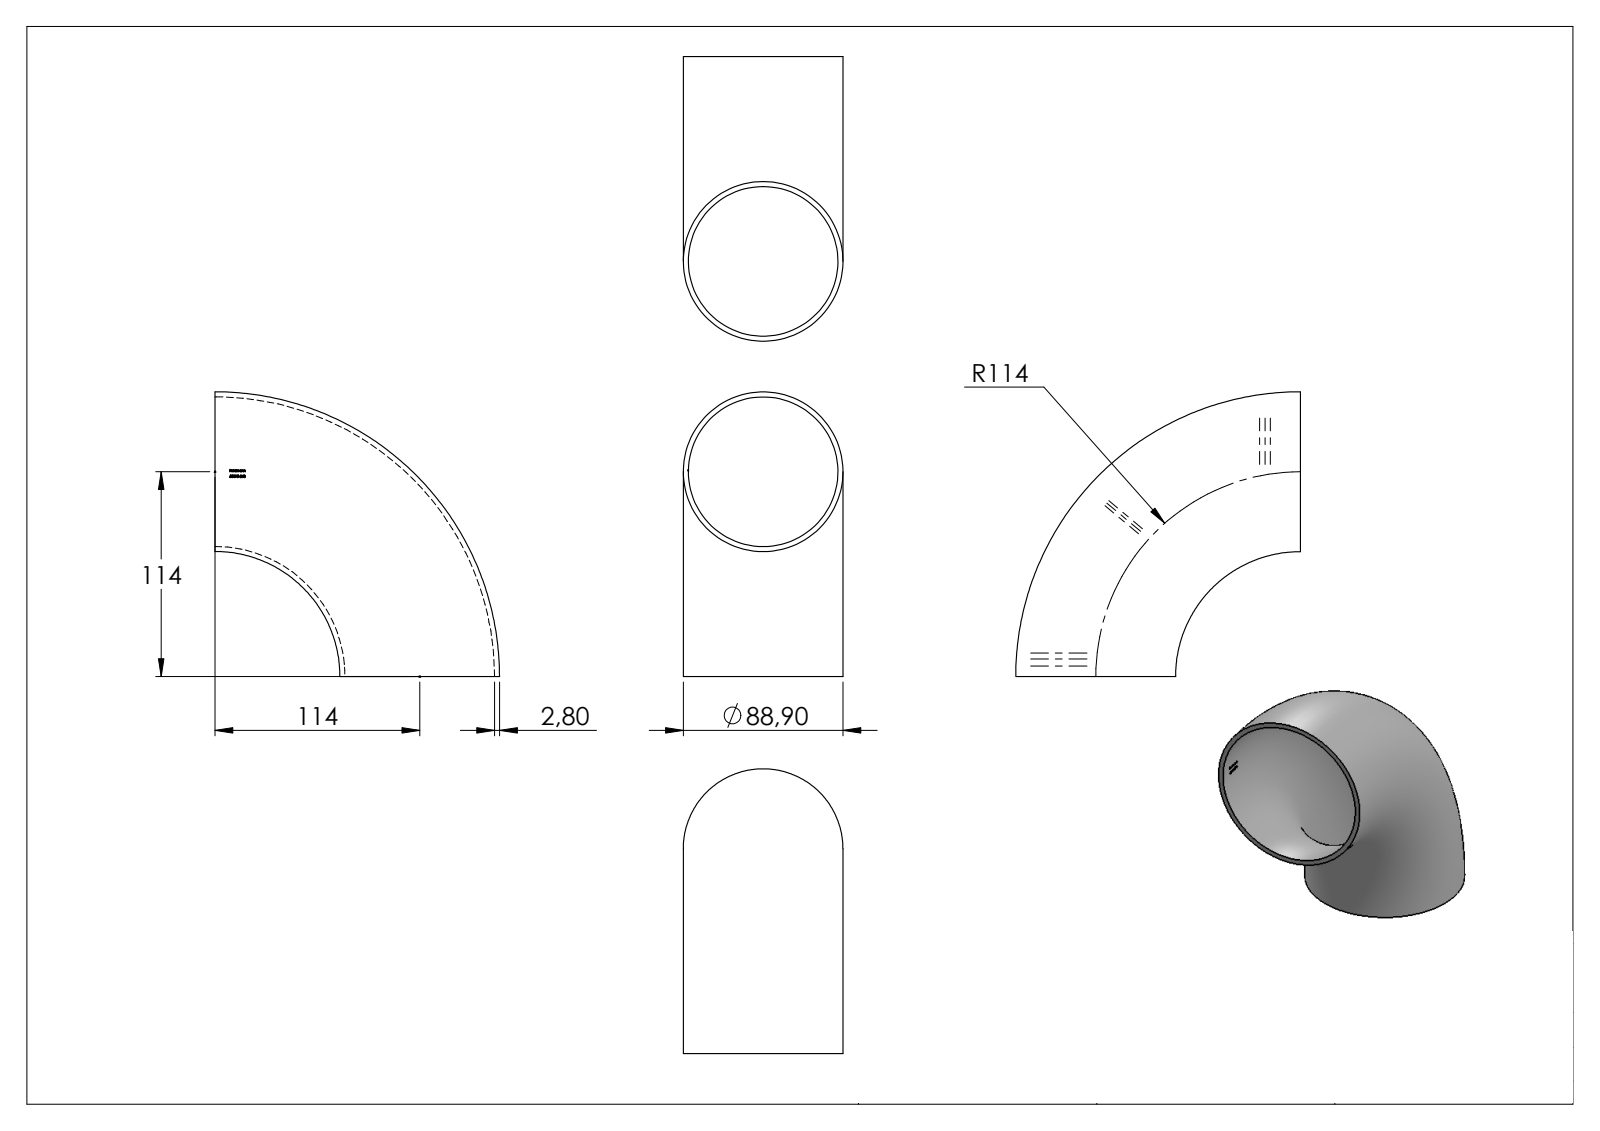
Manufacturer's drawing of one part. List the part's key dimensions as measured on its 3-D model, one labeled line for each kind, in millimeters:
Part name (STEP PRODUCT): 55195-240
STEP written by: SolidWorks 2015 (CONFIG_CONTROL_DESIGN)
Units: millimetres
Bodies: 1 solid, 229 faces (106 planar, 0 cylindrical, 123 other)
Overall size (bounding box): 158.45 × 158.45 × 88.9
Volume: 135 623 mm³ · Surface area: 98 398 mm²
Main face-to-face distances: 0.39, 1.26, 2.97, 1.32, 4.23, 2.02, 3.66, 3.27, 2.4, 0.88
